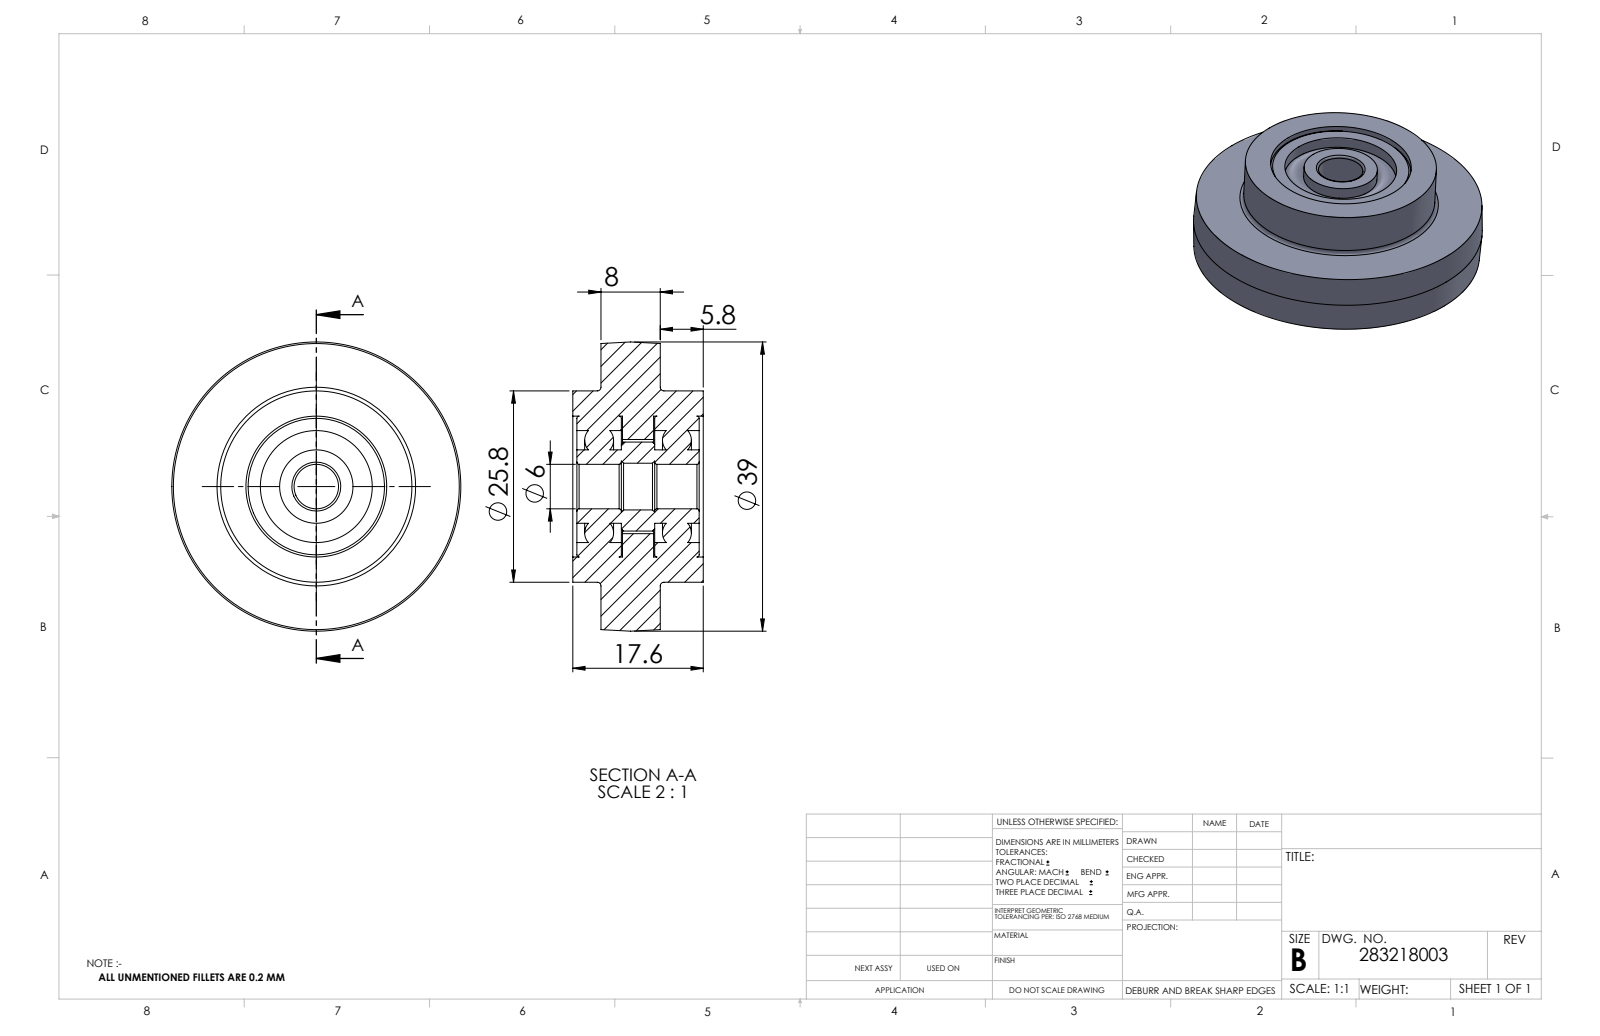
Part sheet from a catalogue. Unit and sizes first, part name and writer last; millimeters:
Units: millimetres
Overall size (bounding box): 39 × 39 × 17.6
Round holes (diameter × count): ⌀6 ×1, ⌀6.3 ×1, ⌀12.7 ×1, ⌀15.1 ×1, ⌀19 ×1
Round bosses / shafts (diameter × count): ⌀25.8 ×1, ⌀12 ×1, ⌀9.9 ×1
Main face-to-face distances: 8, 6.7, 10.9, 0.55, 17.05, 6.15, 10.35, 5.25, 11.8, 3.8
Volume: 13 080 mm³ · Surface area: 6 175 mm²
Bodies: 1 solid, 94 faces (16 planar, 38 cylindrical, 40 other)
Part name (STEP PRODUCT): 283218003_c_1
STEP written by: SolidWorks 2014 (CONFIG_CONTROL_DESIGN)
